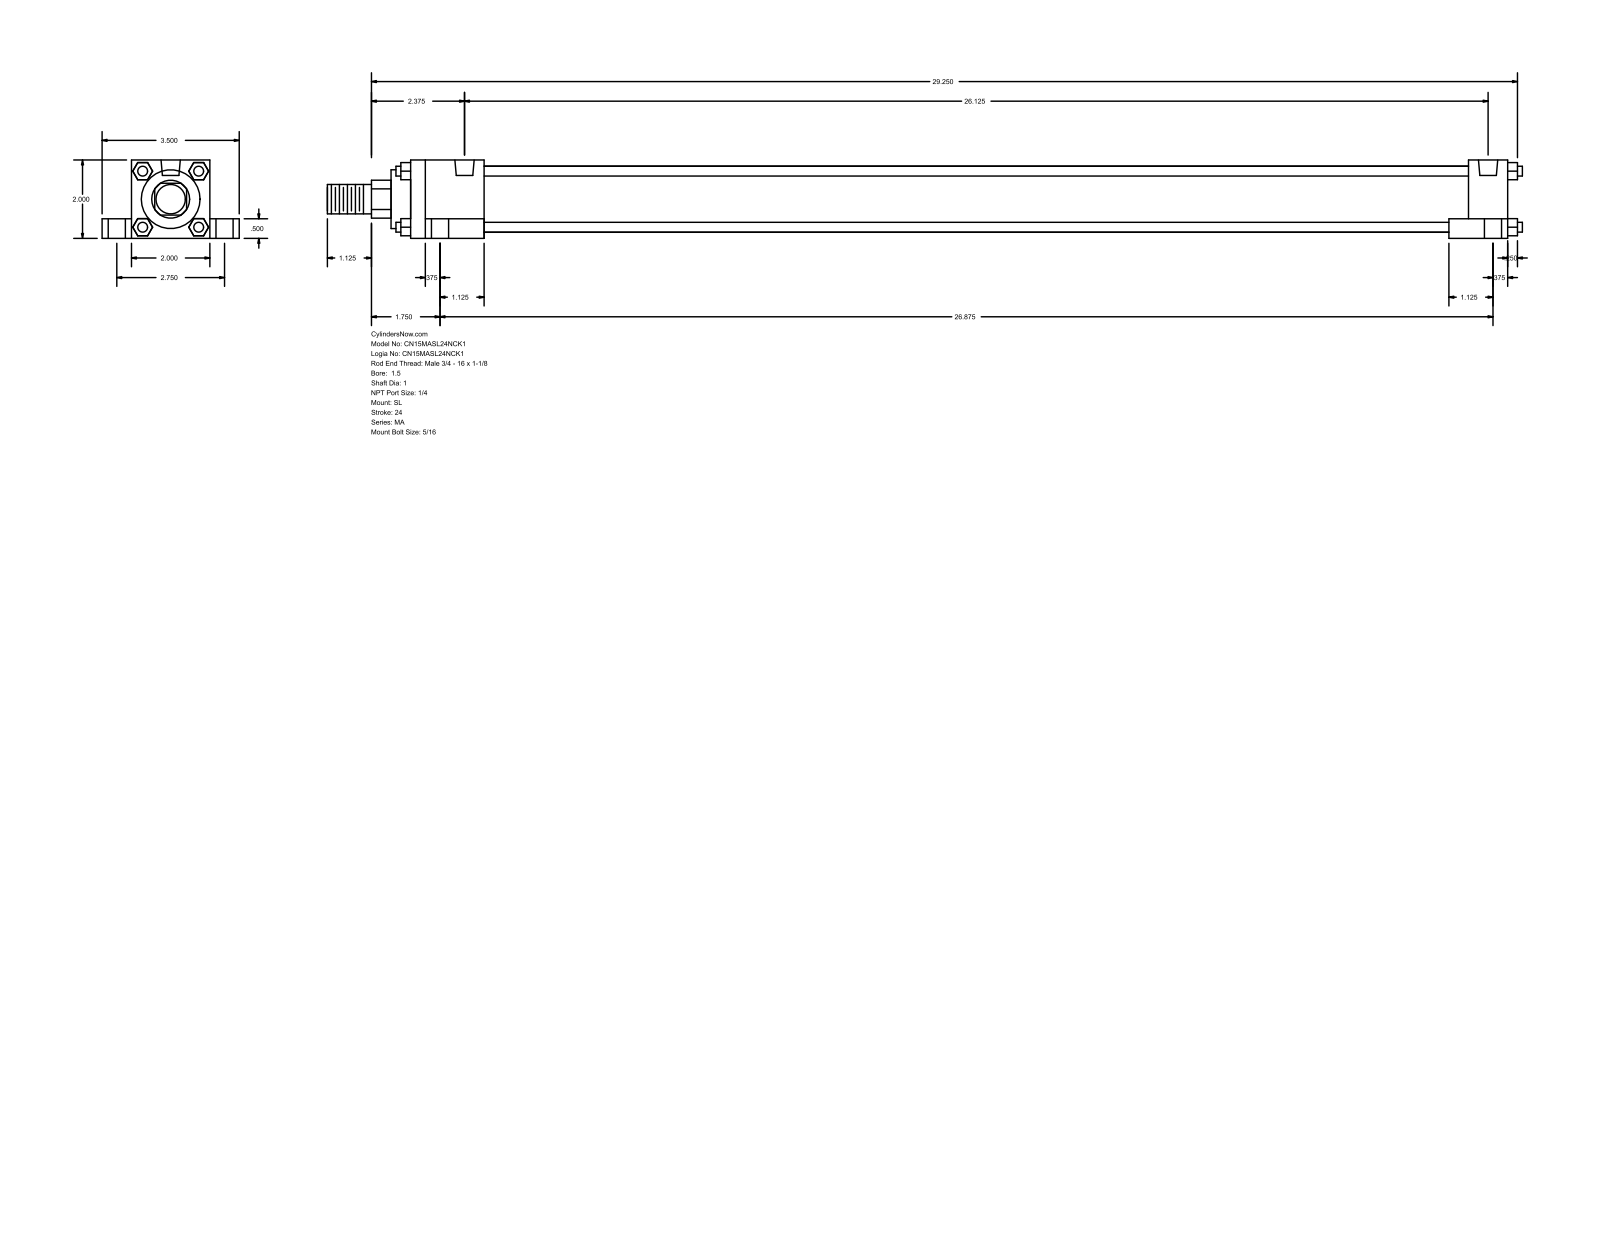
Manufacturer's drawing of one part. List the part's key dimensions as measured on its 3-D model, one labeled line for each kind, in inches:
Part name (STEP PRODUCT): MA_SL__0150_1
STEP written by: GSSL Pune (CONFIG_CONTROL_DESIGN)
Units: inches
Bodies: 0 solids, 148 faces (112 planar, 36 cylindrical, 0 other)
Overall size (bounding box): 30.5 × 3.5 × 2
Round holes (diameter × count): ⌀0.313 ×4, ⌀0.437 ×4, ⌀0.687 ×4, ⌀0.492 ×2
Round bosses / shafts (diameter × count): ⌀0.25 ×4, ⌀1.69 ×1, ⌀1.5 ×1, ⌀1 ×1, ⌀0.75 ×1
Partial cylindrical surfaces — rounded edges, fillets, slot ends (radius × count): R0.484 ×1
Main face-to-face distances: 2, 0.5, 0.75, 2.75, 1.5, 0.375, 28, 1, 0.25, 27
Hole centre spacings: 1.38, 1.51, 2.75, 26.125, 26.286, 26.785, 26.875, 27.015
